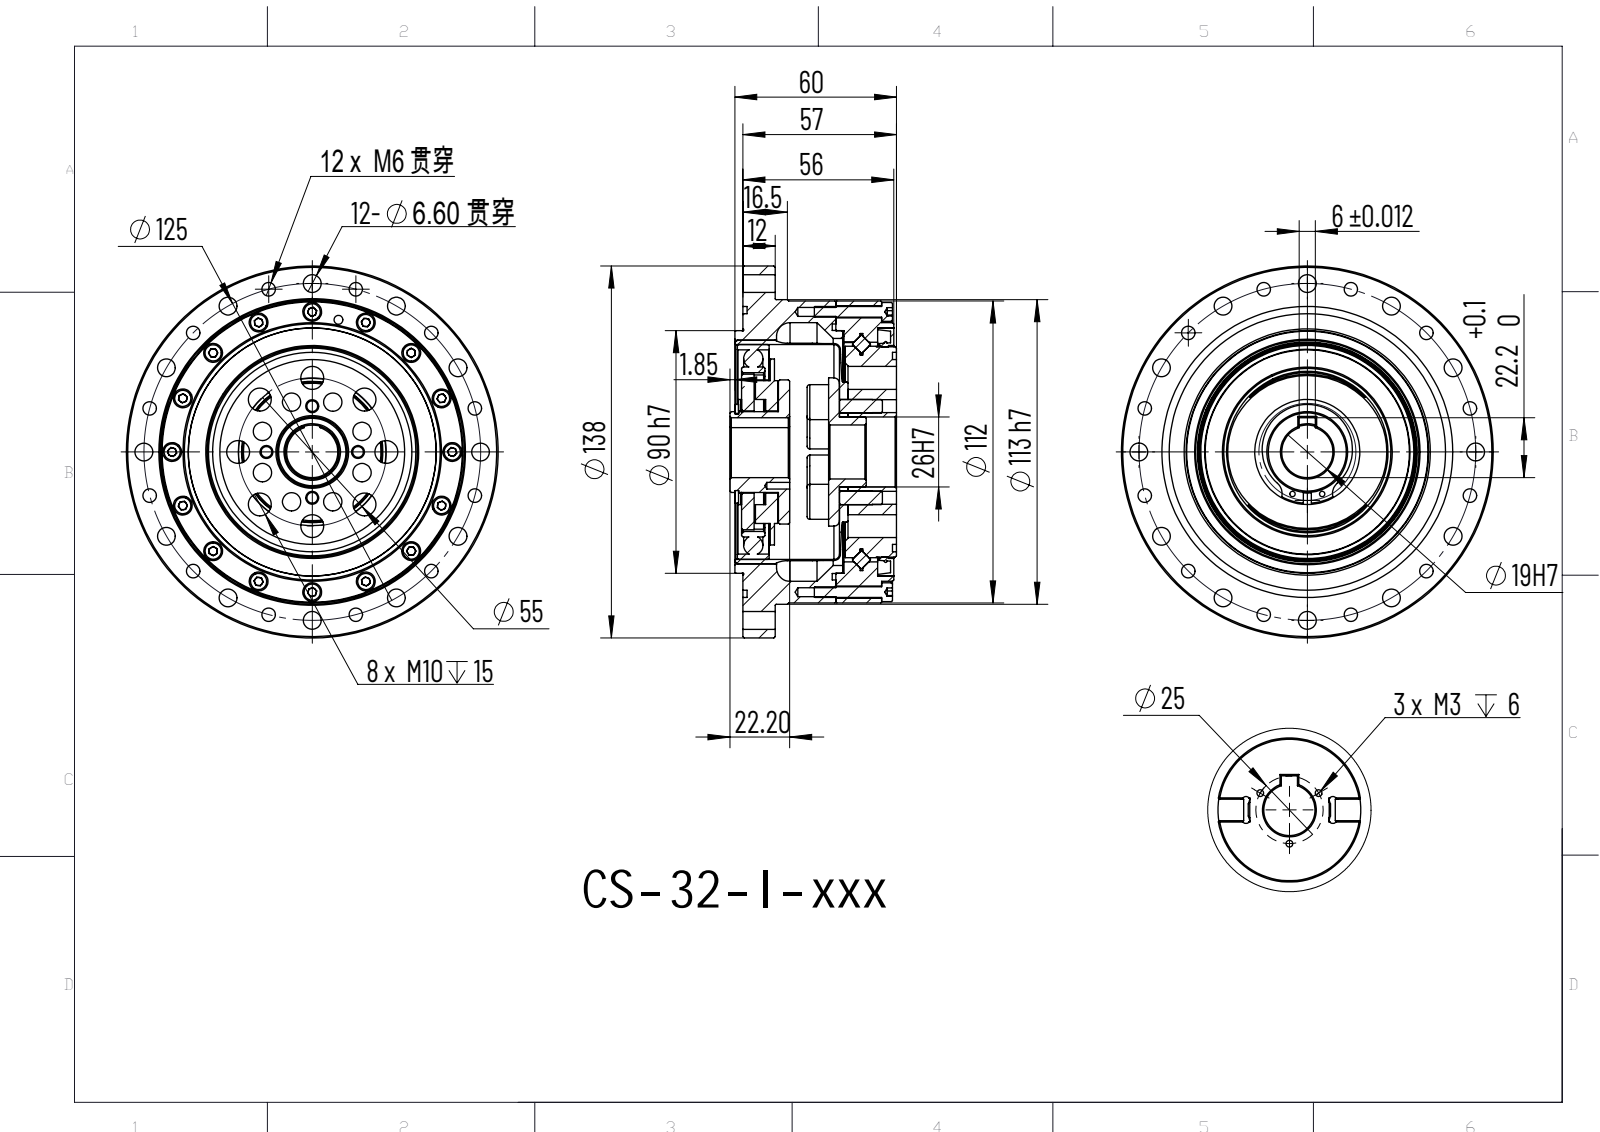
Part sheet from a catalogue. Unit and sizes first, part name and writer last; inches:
Units: inches
Overall size (bounding box): 5.433 × 5.433 × 2.441
Round holes (diameter × count): ⌀0.13 ×20, ⌀0.177 ×20, ⌀0.197 ×20, ⌀0.26 ×12, ⌀0.268 ×8, ⌀0.335 ×8, ⌀0.354 ×8, ⌀0.205 ×4, ⌀0.098 ×3, ⌀0.079 ×2, ⌀0.748 ×1, ⌀0.787 ×1
Round bosses / shafts (diameter × count): ⌀0.197 ×48, ⌀0.276 ×20, ⌀0.157 ×20, ⌀0.512 ×8, ⌀0.315 ×8, ⌀5.433 ×1, ⌀4.449 ×1, ⌀4.409 ×1
Partial cylindrical surfaces — rounded edges, fillets, slot ends (radius × count): R0.02 ×2, R0.039 ×2, R0.482 ×1, R0.571 ×1
Main face-to-face distances: 1.732, 0.472, 1.358, 0.886, 0.669, 0.177, 1.535, 0.374, 0.236, 0.059
Hole centre spacings: 2.461, 1.712, 1.822, 2.771, 2.935, 4.754, 1.274, 1.983
Volume: 25.43 in³ · Surface area: 333.3 in²
Bodies: 94 solids, 1277 faces (689 planar, 308 cylindrical, 280 other)
Part name (STEP PRODUCT): CS-32-I; hexagon socket head cap screws gb_GB_FASTENER_SCREWS_HSHCS M4X12-C; 32-80??; hexagon socket head cap screws gb_GB_FASTENER_SCREWS_HSHCS M8X20-C (+8 more)
STEP written by: ONSHAPE BY PTC INC, 1.201 (AP242_MANAGED_MODEL_BASED_3D_ENGINEERING_MIM_LF)
